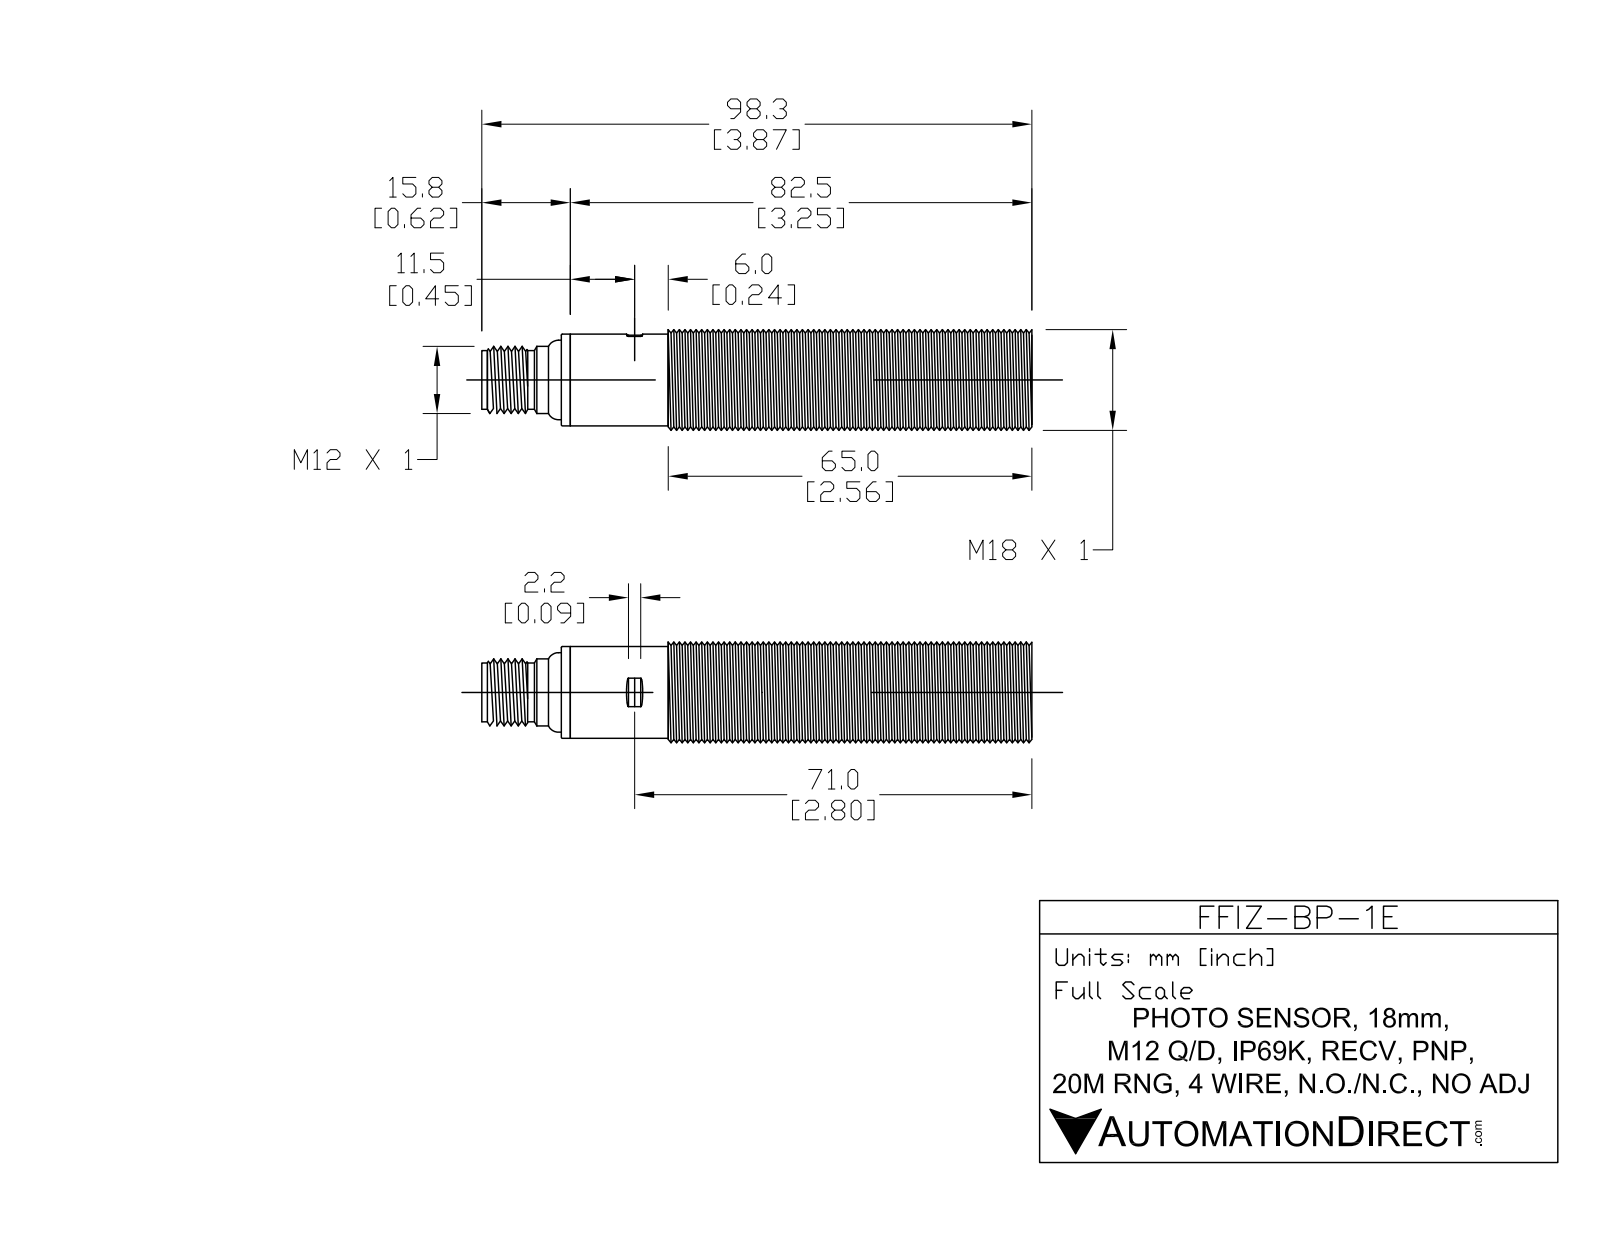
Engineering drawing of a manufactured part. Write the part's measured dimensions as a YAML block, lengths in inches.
part_name: "FFIZ-BP-1E"
step_written_by: "SolidWorks 2017 (AUTOMOTIVE_DESIGN)"
units: inches
bodies: {solids: 5, faces: 118, planar: 21, cylindrical: 48, other: 49}
overall_size: [3.268, 0.709, 0.709]
volume: 1.081
surface_area: 10.47
round_holes:
  - {diameter: 0.278, count: 1}
  - {diameter: 0.327, count: 1}
  - {diameter: 0.5, count: 1}
  - {diameter: 0.583, count: 1}
  - {diameter: 0.61, count: 1}
round_bosses_or_shafts:
  - {diameter: 0.039, count: 4}
  - {diameter: 0.709, count: 1}
  - {diameter: 0.646, count: 1}
  - {diameter: 0.612, count: 1}
  - {diameter: 0.604, count: 1}
  - {diameter: 0.559, count: 1}
  - {diameter: 0.492, count: 1}
  - {diameter: 0.472, count: 1}
partial_cylinders:
  - {radius: 0.024, count: 1}
  - {radius: 0.63, count: 1}
face_to_face_distances: [2.539, 0.118, 2.657, 0.024, 0.094, 2.634, 2.717, 2.693, 2.598, 0.059]
